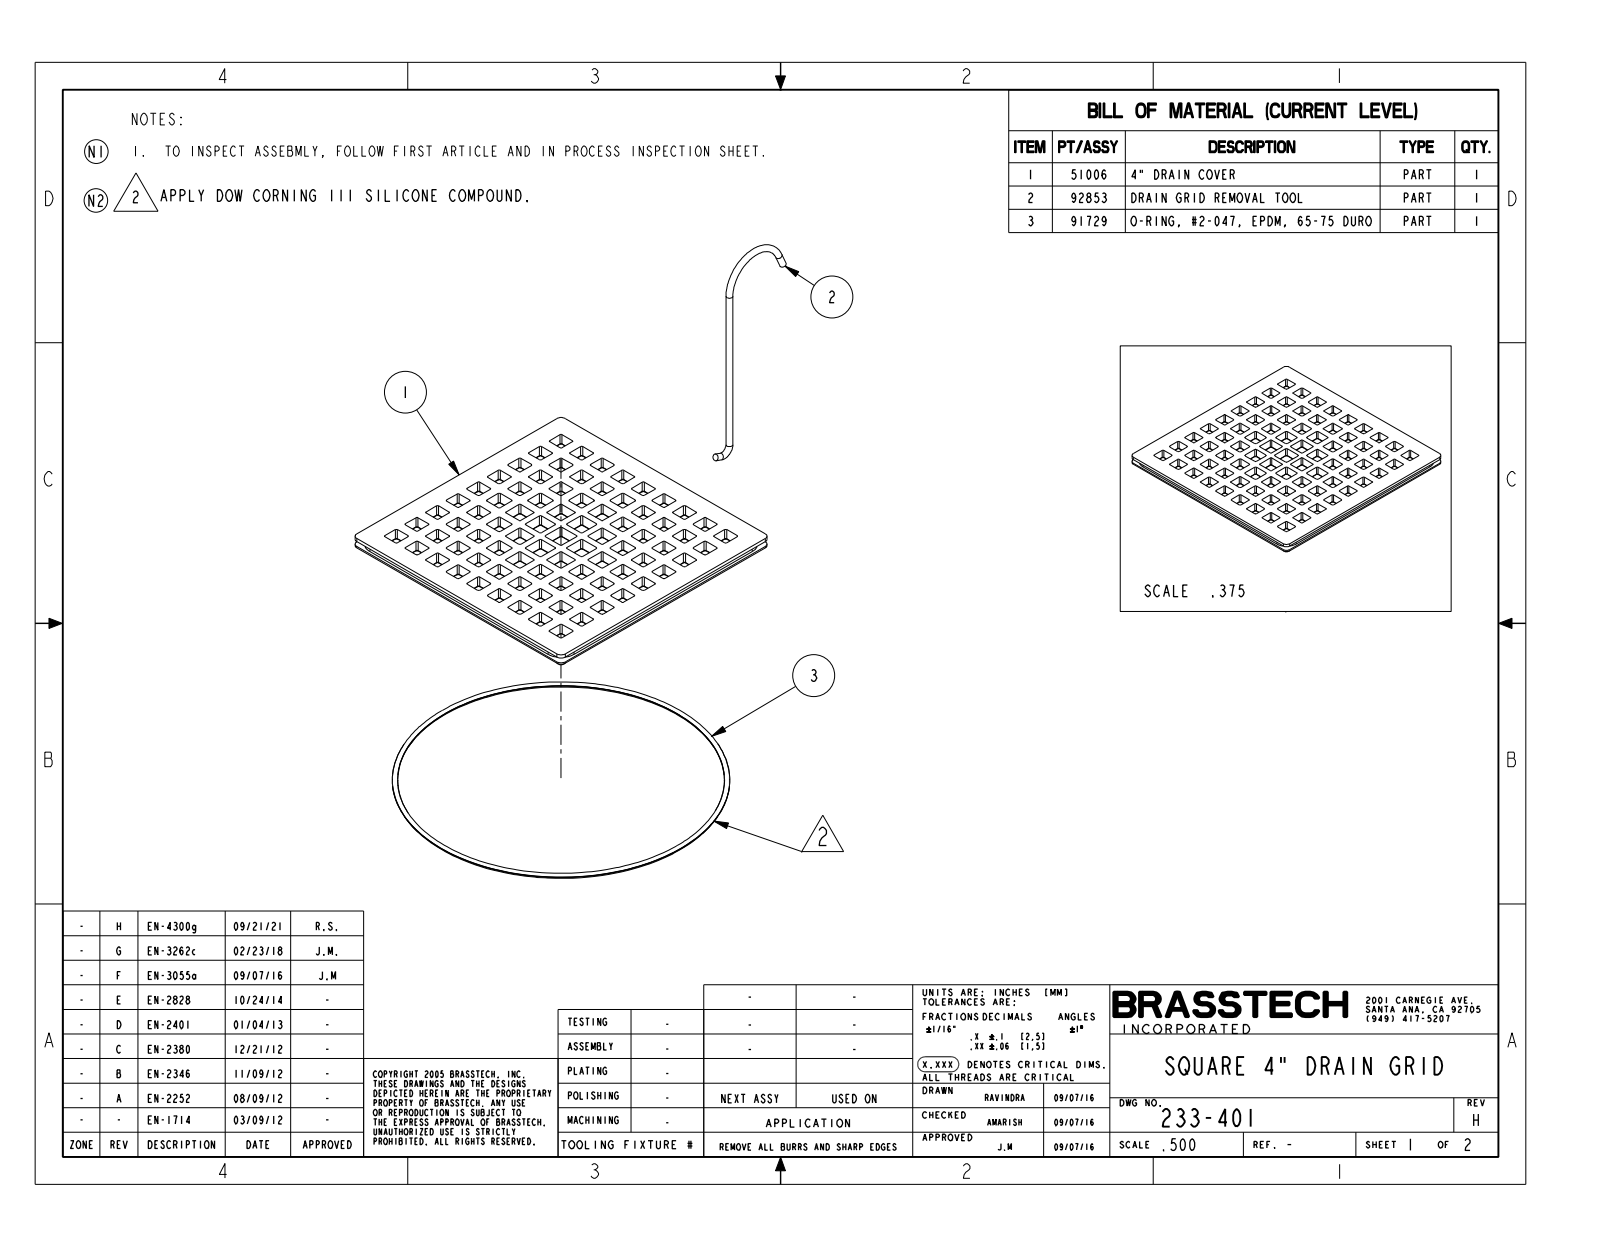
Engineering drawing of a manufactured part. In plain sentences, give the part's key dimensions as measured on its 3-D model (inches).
The part is named "51006". Its 3-D file was written by "CREO PARAMETRIC BY PTC INC, 2018400 (AUTOMOTIVE_DESIGN)". It is 1 solid with 1332 faces: 344 planar, 660 cylindrical and 328 other. Overall it measures 4.045 by 4.045 by 0.188 inches. Its volume is 1.892 cubic inches and its surface area 40.34 square inches. Partial cylindrical surfaces (rounded edges, fillets, slot ends): 426 of radius 0.02, 4 of radius 0.08, 4 of radius 0.25. The main face-to-face distances are 0.398, 0.188, 0.796, 1.194, 1.592, 1.99, 2.388, 2.786, 0.39, 0.406.
